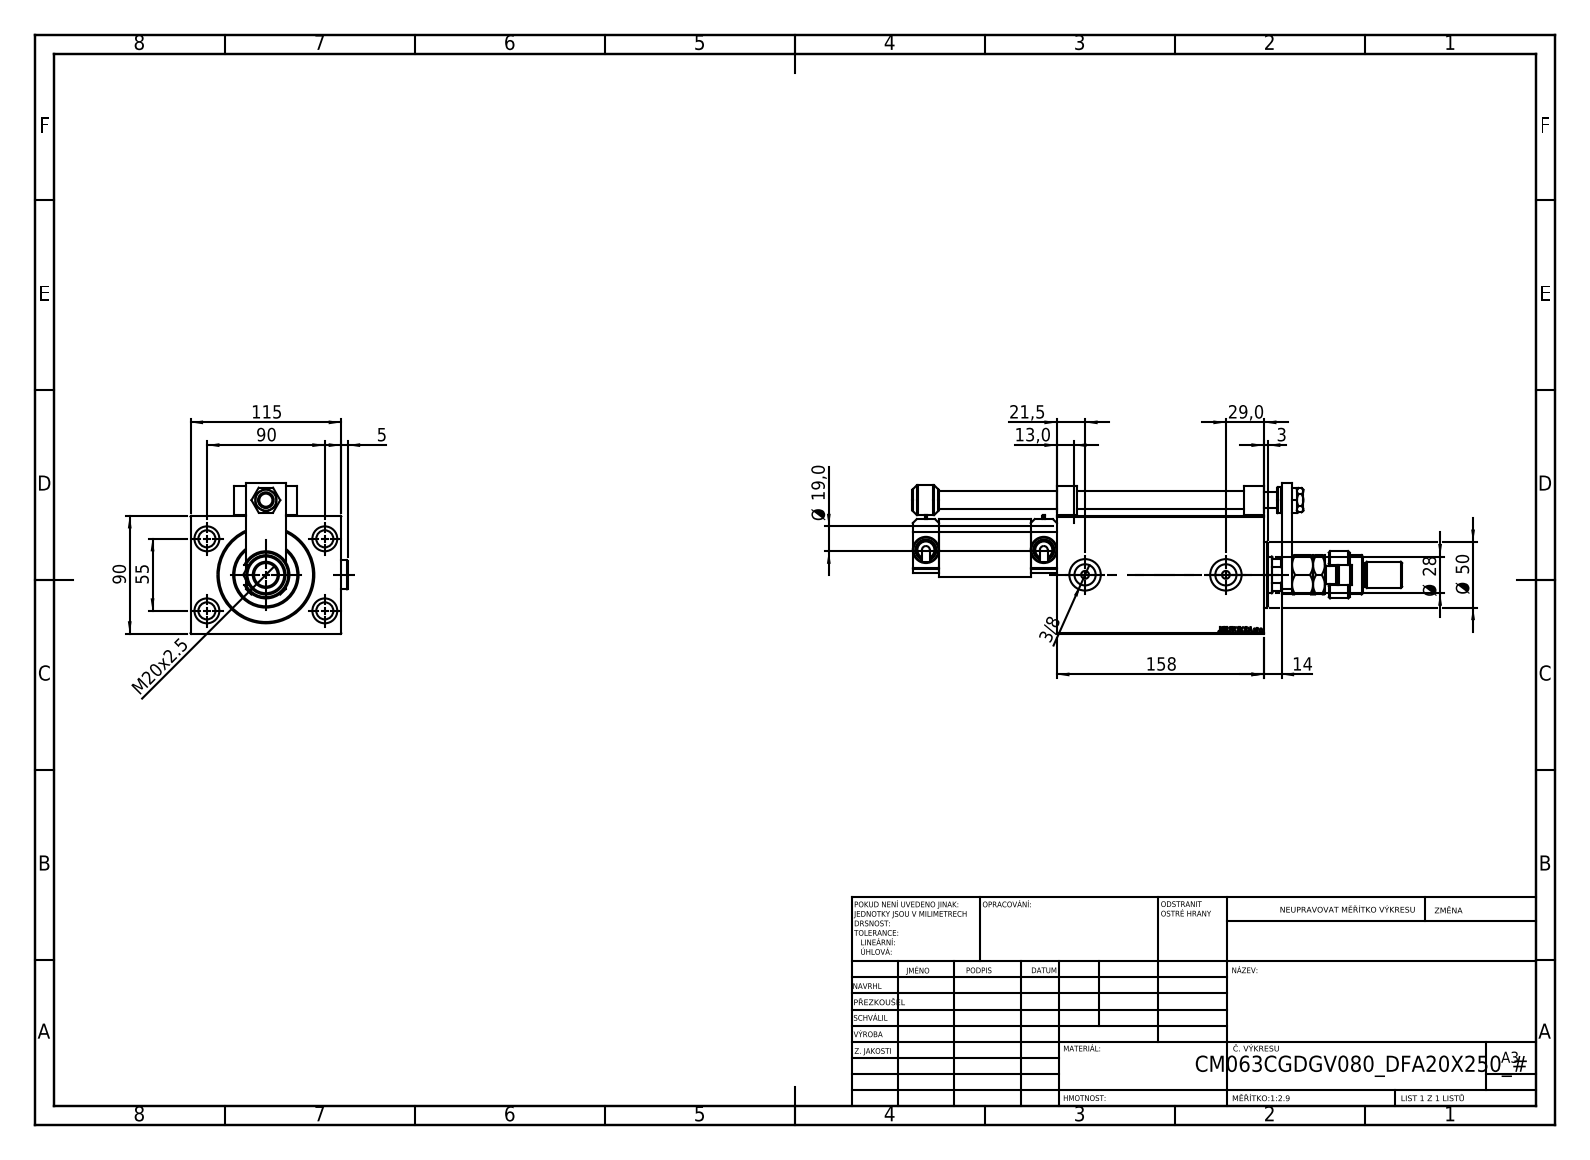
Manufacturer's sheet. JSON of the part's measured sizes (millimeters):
{"part_name": "SWITCH P; ZARAZKA_P; SWITCH DIM W_B; KROUZEK_PRO_TYC (+8 more)", "step_written_by": "SolidWorks 2019 (CONFIG_CONTROL_DESIGN)", "units": "millimeters", "bodies": {"solids": 18, "faces": 1229, "planar": 583, "cylindrical": 149, "other": 497}, "overall_size": [373.8, 119.9, 115], "volume_mm3": 1654000, "surface_area_mm2": 259838, "round_holes": [[13, 5], [4, 4], [8, 4], [19, 4], [6, 2], [16.17, 2], [24, 2], [12, 1], [14, 1], [18.5, 1], [20, 1], [28, 1]], "round_bosses_or_shafts": [[22, 3], [20, 3], [14, 3], [16, 2], [6, 2], [50, 1], [36, 1], [30, 1]], "partial_cylinders_radius": [[3, 1], [7.5, 1], [12, 1], [13.5, 1]], "face_to_face_distances": [90, 115, 37.5, 158, 17.5, 77.5, 13.5, 140.5, 46.5, 35], "hole_center_spacings": [52.74, 20, 53.81, 55, 90, 95.74, 105.48, 143]}
